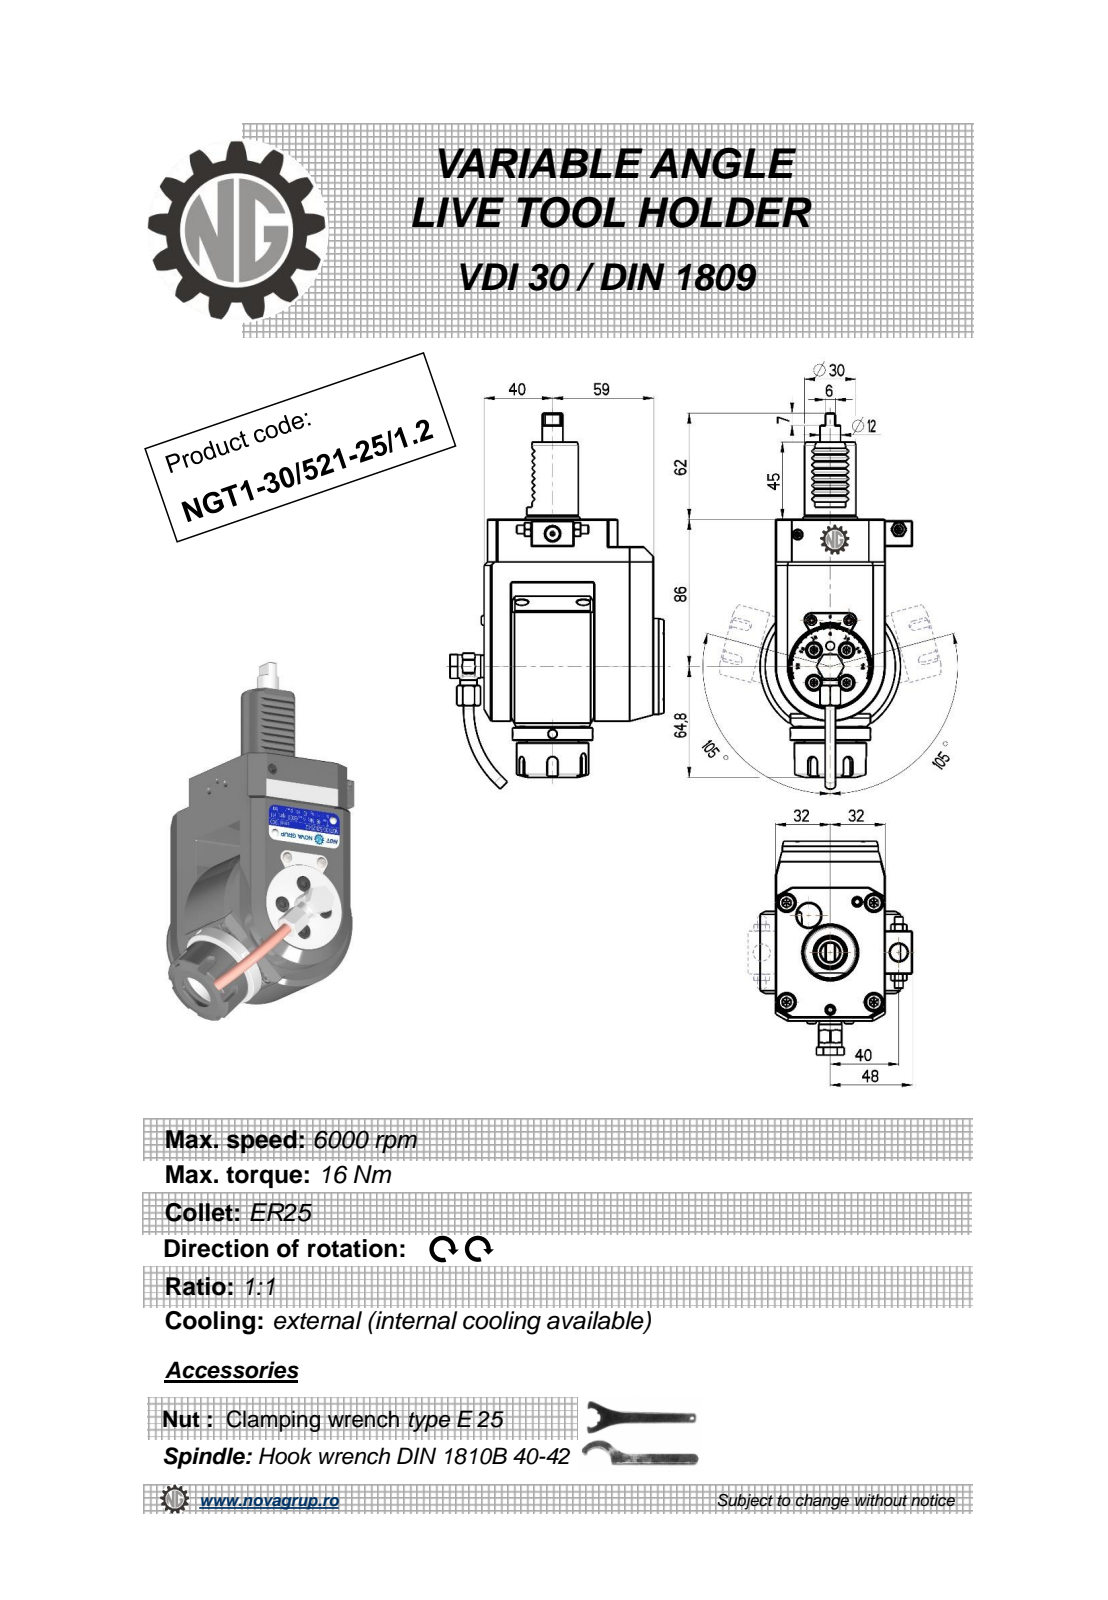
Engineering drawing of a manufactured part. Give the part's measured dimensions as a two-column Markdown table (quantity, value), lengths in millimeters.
| quantity | value |
| --- | --- |
| part name | NGT1_30_521_25_1_2 |
| STEP written by | PRO/ENGINEER BY PARAMETRIC TECHNOLOGY CORPORATION, 2010280 (CONFIG_CONTROL_DESIGN) |
| units | millimeters |
| bodies | 1 solid, 544 faces (229 planar, 132 cylindrical, 183 other) |
| overall size | 219.67 × 124.9 × 89 |
| volume | 779 434 mm³ |
| surface area | 74 506 mm² |
| round holes (diameter × count) | 4 × 3, 5 × 2, 10 × 2, 3 × 1, 4.2 × 1, 6.2 × 1, 9 × 1, 9.5 × 1, 11 × 1, 20.3 × 1 |
| round bosses / shafts (diameter × count) | 6 × 2, 5.7 × 2, 82 × 1, 56 × 1, 47 × 1, 42 × 1, 35 × 1, 30 × 1 |
| partial cylindrical surfaces (radius × count) | 0.26 × 12, 0.3 × 8, 0.16 × 6, 0.5 × 6, 3 × 5, 1 × 2, 7.7 × 1, 32 × 1 |
| main face-to-face distances | 64, 16, 37, 6, 99, 105, 21, 35, 14, 41 |
| hole center spacings | 0.4, 39.45, 40, 49, 49.4, 63.25, 63.56, 89.44 |
